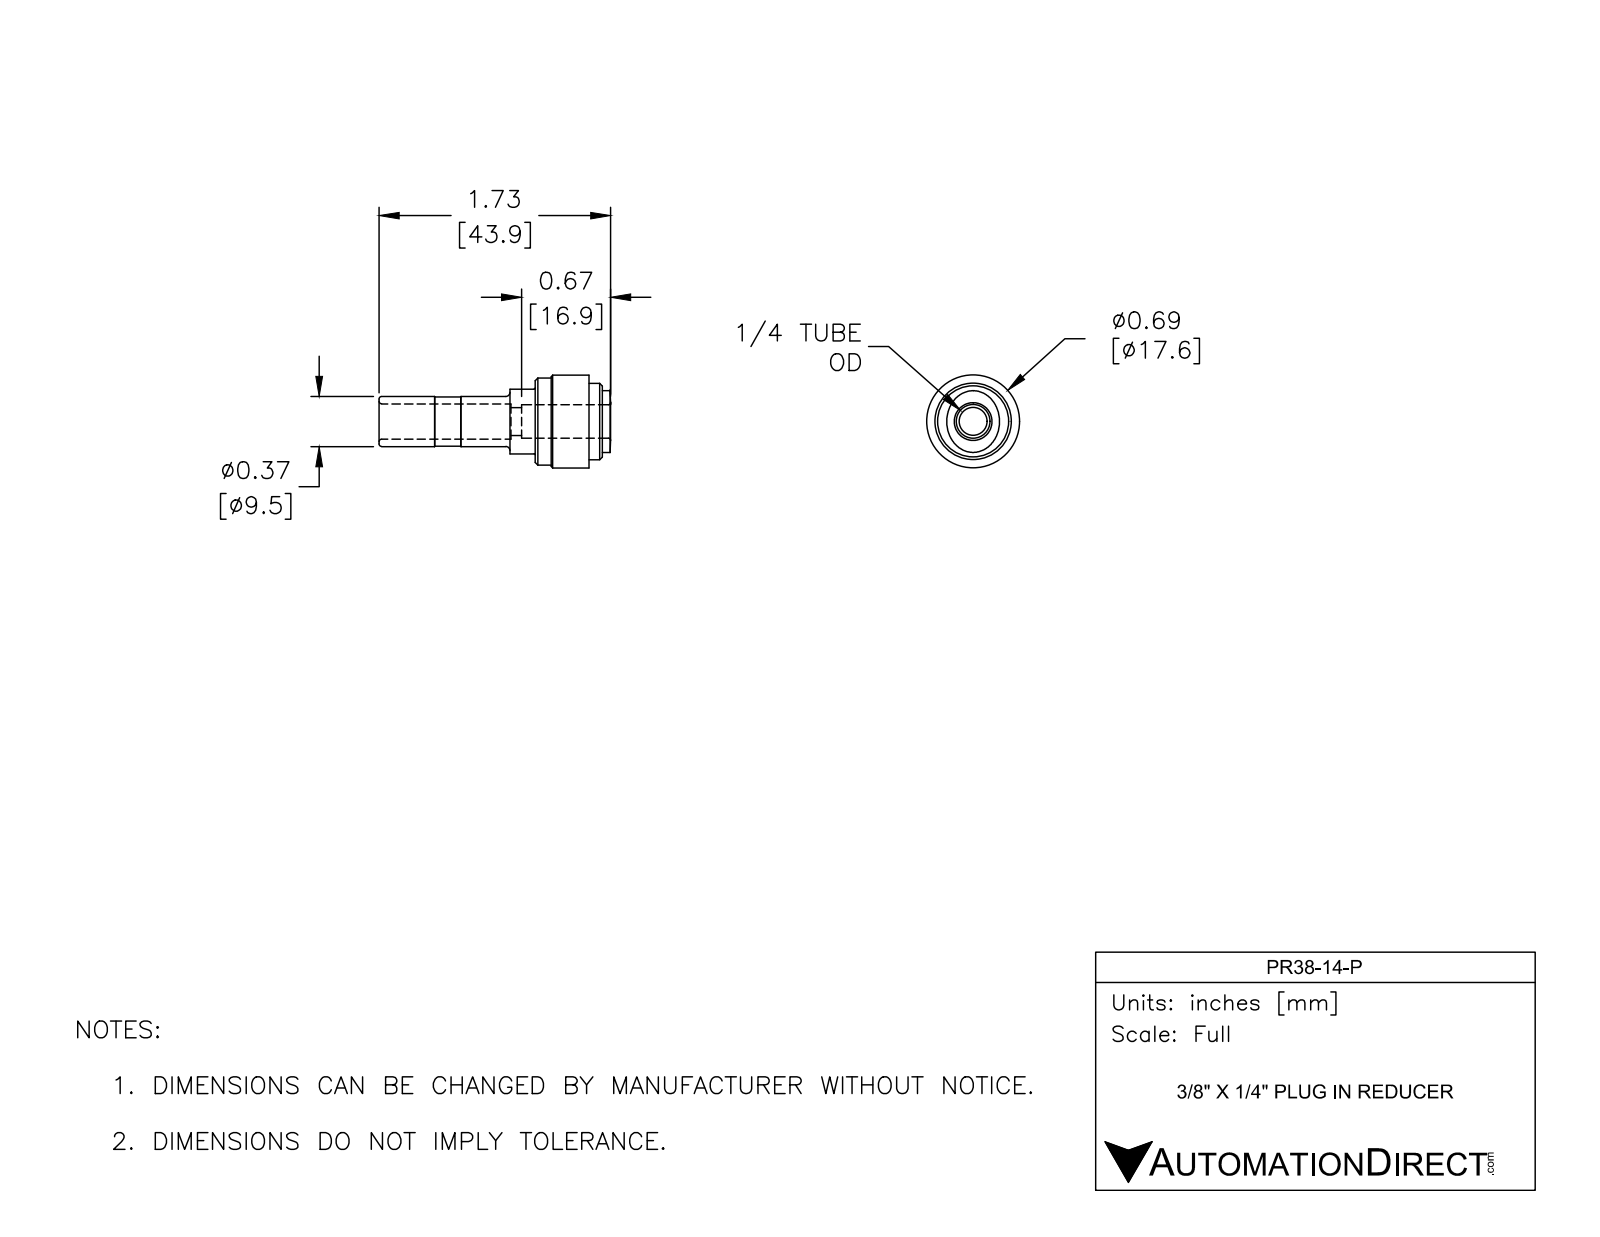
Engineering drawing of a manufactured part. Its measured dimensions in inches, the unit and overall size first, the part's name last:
Units: inches
Overall size (bounding box): 1.728 × 0.693 × 0.693
Round holes (diameter × count): ⌀0.209 ×1, ⌀0.25 ×1, ⌀0.264 ×1
Round bosses / shafts (diameter × count): ⌀0.693 ×1, ⌀0.65 ×1, ⌀0.571 ×1, ⌀0.484 ×1, ⌀0.374 ×1, ⌀0.368 ×1
Main face-to-face distances: 0.402, 0.5, 0.098, 0.189, 0.591, 0.689, 0.181, 0.583, 0.681, 0.307
Volume: 0.232 in³ · Surface area: 4.521 in²
Bodies: 1 solid, 52 faces (8 planar, 20 cylindrical, 24 other)
Part name (STEP PRODUCT): PR38-14-P
STEP written by: SolidWorks 2017 (AUTOMOTIVE_DESIGN)
